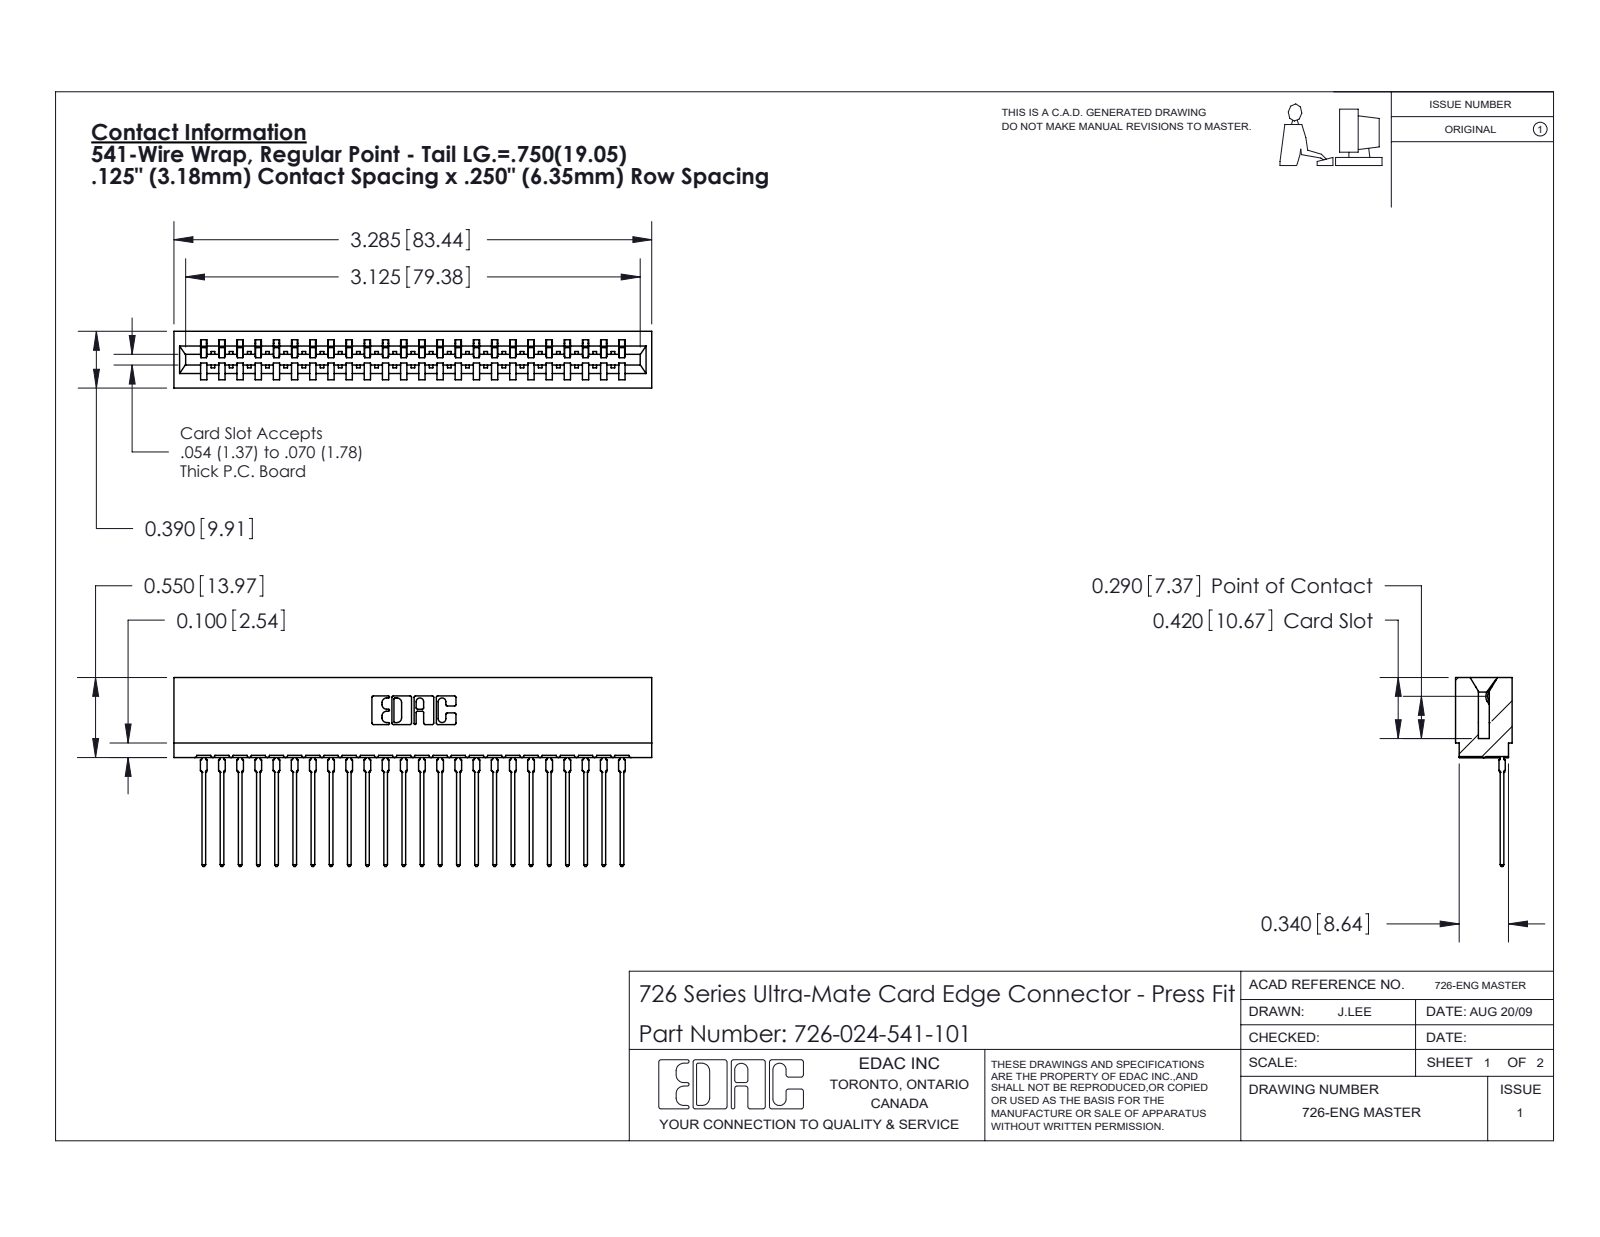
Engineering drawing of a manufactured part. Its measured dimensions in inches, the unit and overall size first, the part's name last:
Units: inches
Overall size (bounding box): 3.285 × 1.299 × 0.39
Partial cylindrical surfaces — rounded edges, fillets, slot ends (radius × count): R0.021 ×48, R0.015 ×25, R0.01 ×22, R0.007 ×6, R0.031 ×6, R0.005 ×4, R0.011 ×4, R0.026 ×3
Main face-to-face distances: 0.057, 0.333, 0.39, 0.025, 0.307, 0.25, 0.083, 0.042, 0.75, 0.275
Volume: 0.468 in³ · Surface area: 18.62 in²
Bodies: 25 solids, 2689 faces (1567 planar, 498 cylindrical, 624 other)
Part name (STEP PRODUCT): 726 Part_.515 Slot Depth - 01; 726-024-541-101; 746-292-001_541
STEP written by: SolidWorks 2020 (CONFIG_CONTROL_DESIGN)
